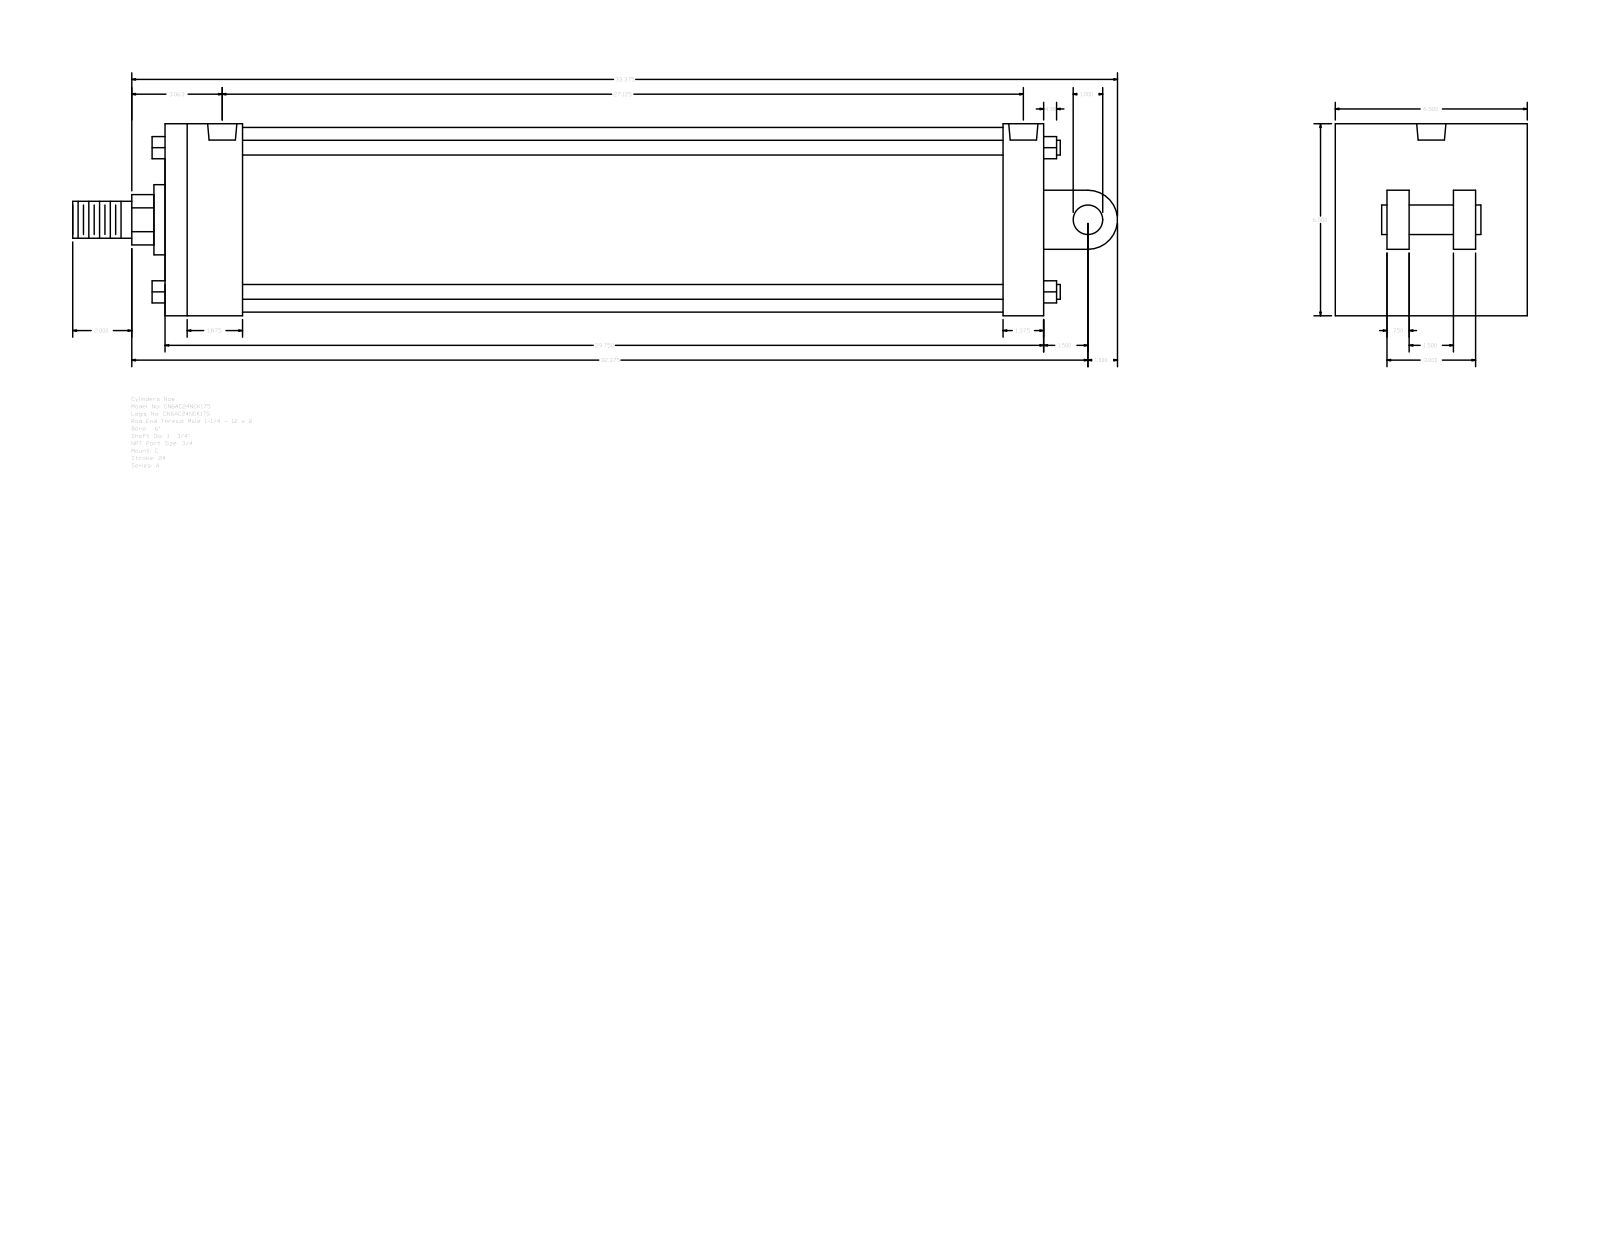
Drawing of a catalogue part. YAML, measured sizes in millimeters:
part_name: "A_C__0600_1.75"
step_written_by: "GSSL Pune (CONFIG_CONTROL_DESIGN)"
units: millimeters
bodies: {solids: 0, faces: 135, planar: 102, cylindrical: 33, other: 0}
overall_size: [898.52, 165.1, 165.1]
round_holes:
  - {diameter: 15.08, count: 4}
  - {diameter: 25.12, count: 2}
round_bosses_or_shafts:
  - {diameter: 12.7, count: 4}
  - {diameter: 158.75, count: 1}
  - {diameter: 60.33, count: 1}
  - {diameter: 44.45, count: 1}
  - {diameter: 31.75, count: 1}
  - {diameter: 25.4, count: 1}
partial_cylinders:
  - {radius: 21.63, count: 1}
  - {radius: 25.4, count: 1}
face_to_face_distances: [165.1, 755.66, 19.05, 57.15, 66.68, 688.98, 720.73, 654.05, 34.93, 63.5]
hole_center_spacings: [5.56, 677.85, 683.41, 688.97]
